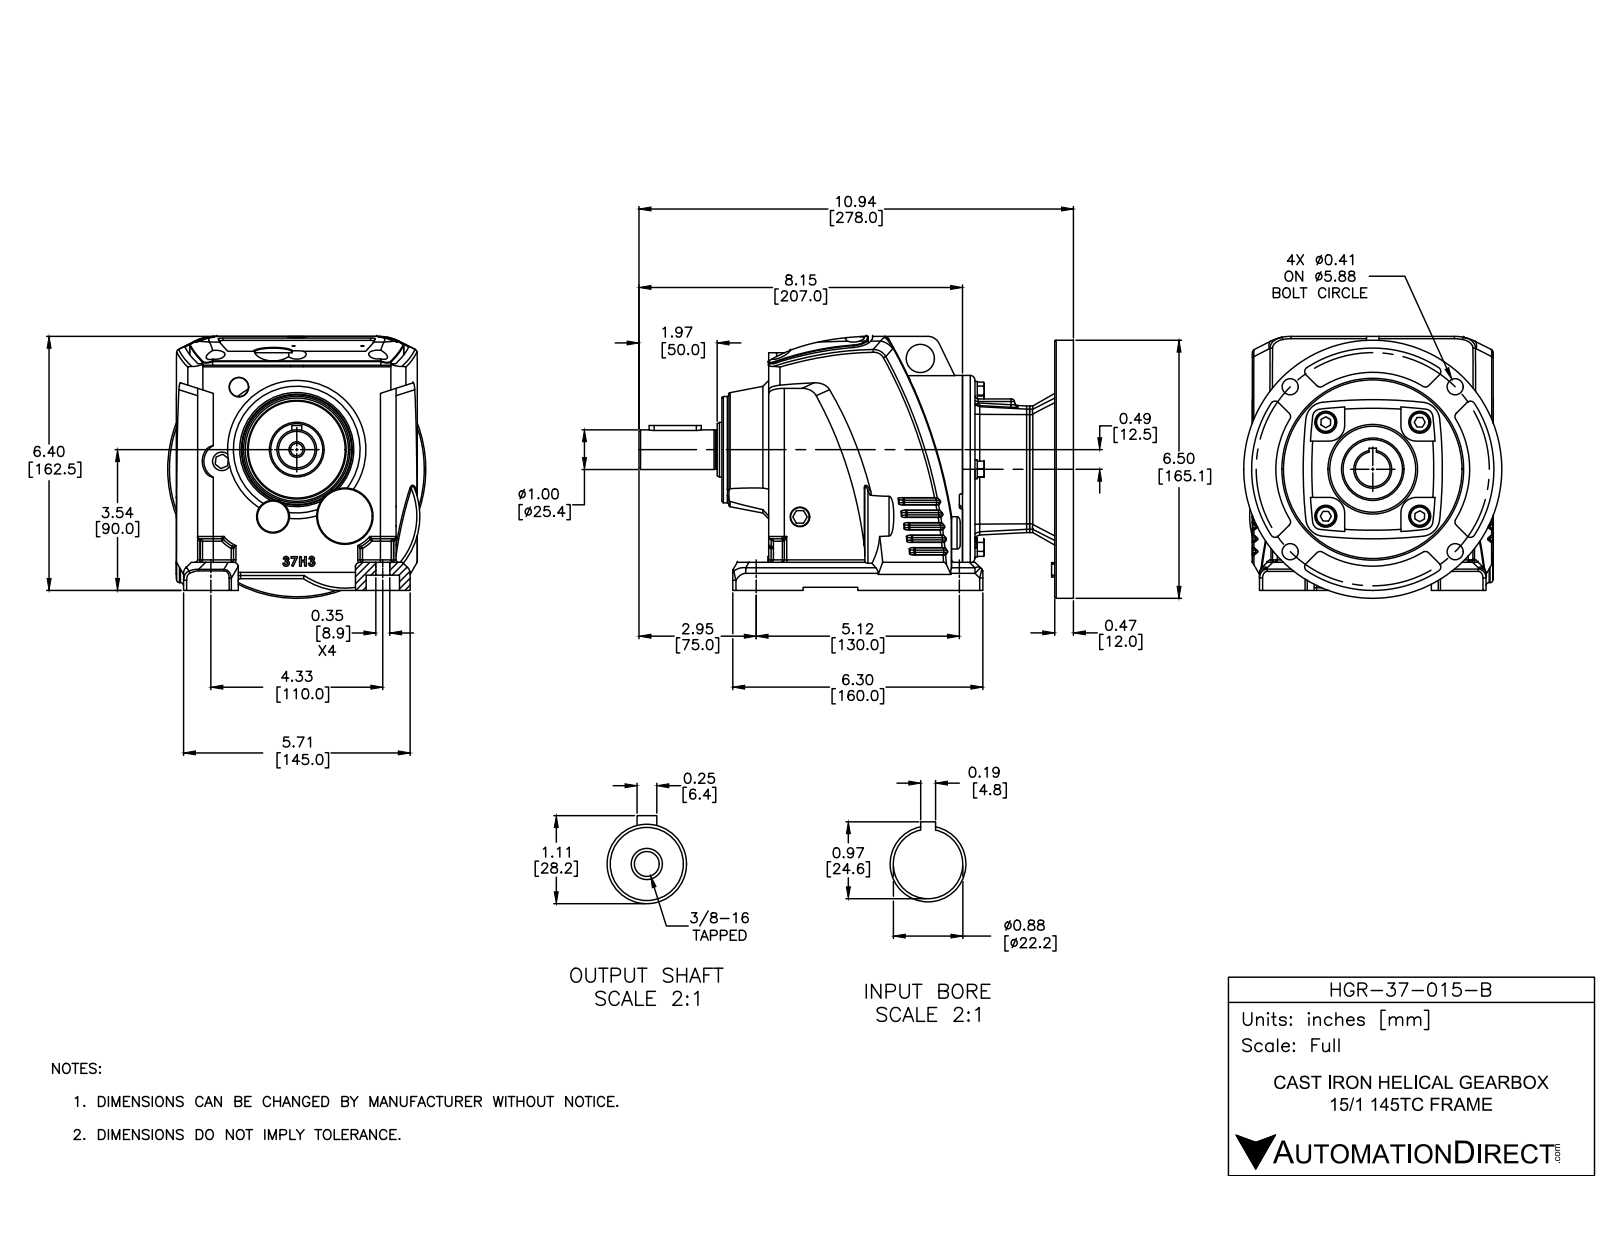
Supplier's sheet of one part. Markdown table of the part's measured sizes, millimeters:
| quantity | value |
| --- | --- |
| part name | HGR-37-015-B |
| STEP written by | SolidWorks 2015 (CONFIG_CONTROL_DESIGN) |
| units | millimeters |
| bodies | 28 solids, 1025 faces (348 planar, 289 cylindrical, 388 other) |
| overall size | 278 × 167.5 × 165.1 |
| volume | 3 066 000 mm³ |
| surface area | 308 500 mm² |
| round holes (diameter × count) | 12 × 6, 10.3 × 4, 14 × 4, 7 × 3, 2 × 2, 9 × 2, 10 × 2, 8 × 1, 13.5 × 1, 18 × 1, 22.2 × 1, 35 × 1 |
| round bosses / shafts (diameter × count) | 13 × 7, 12.2 × 4, 165.1 × 1, 120 × 1, 68 × 1, 62 × 1, 55 × 1, 35 × 1 |
| partial cylindrical surfaces (radius × count) | 1.5 × 43, 3 × 19, 2 × 18, 10 × 10, 5 × 8, 8 × 5, 4 × 4, 7 × 4 |
| main face-to-face distances | 7, 16, 59, 28, 190, 43, 183, 8, 23, 66 |
| hole center spacings | 32.1, 42.5, 74.6, 85.9, 85.9, 117.1, 34.8, 47.4 |
